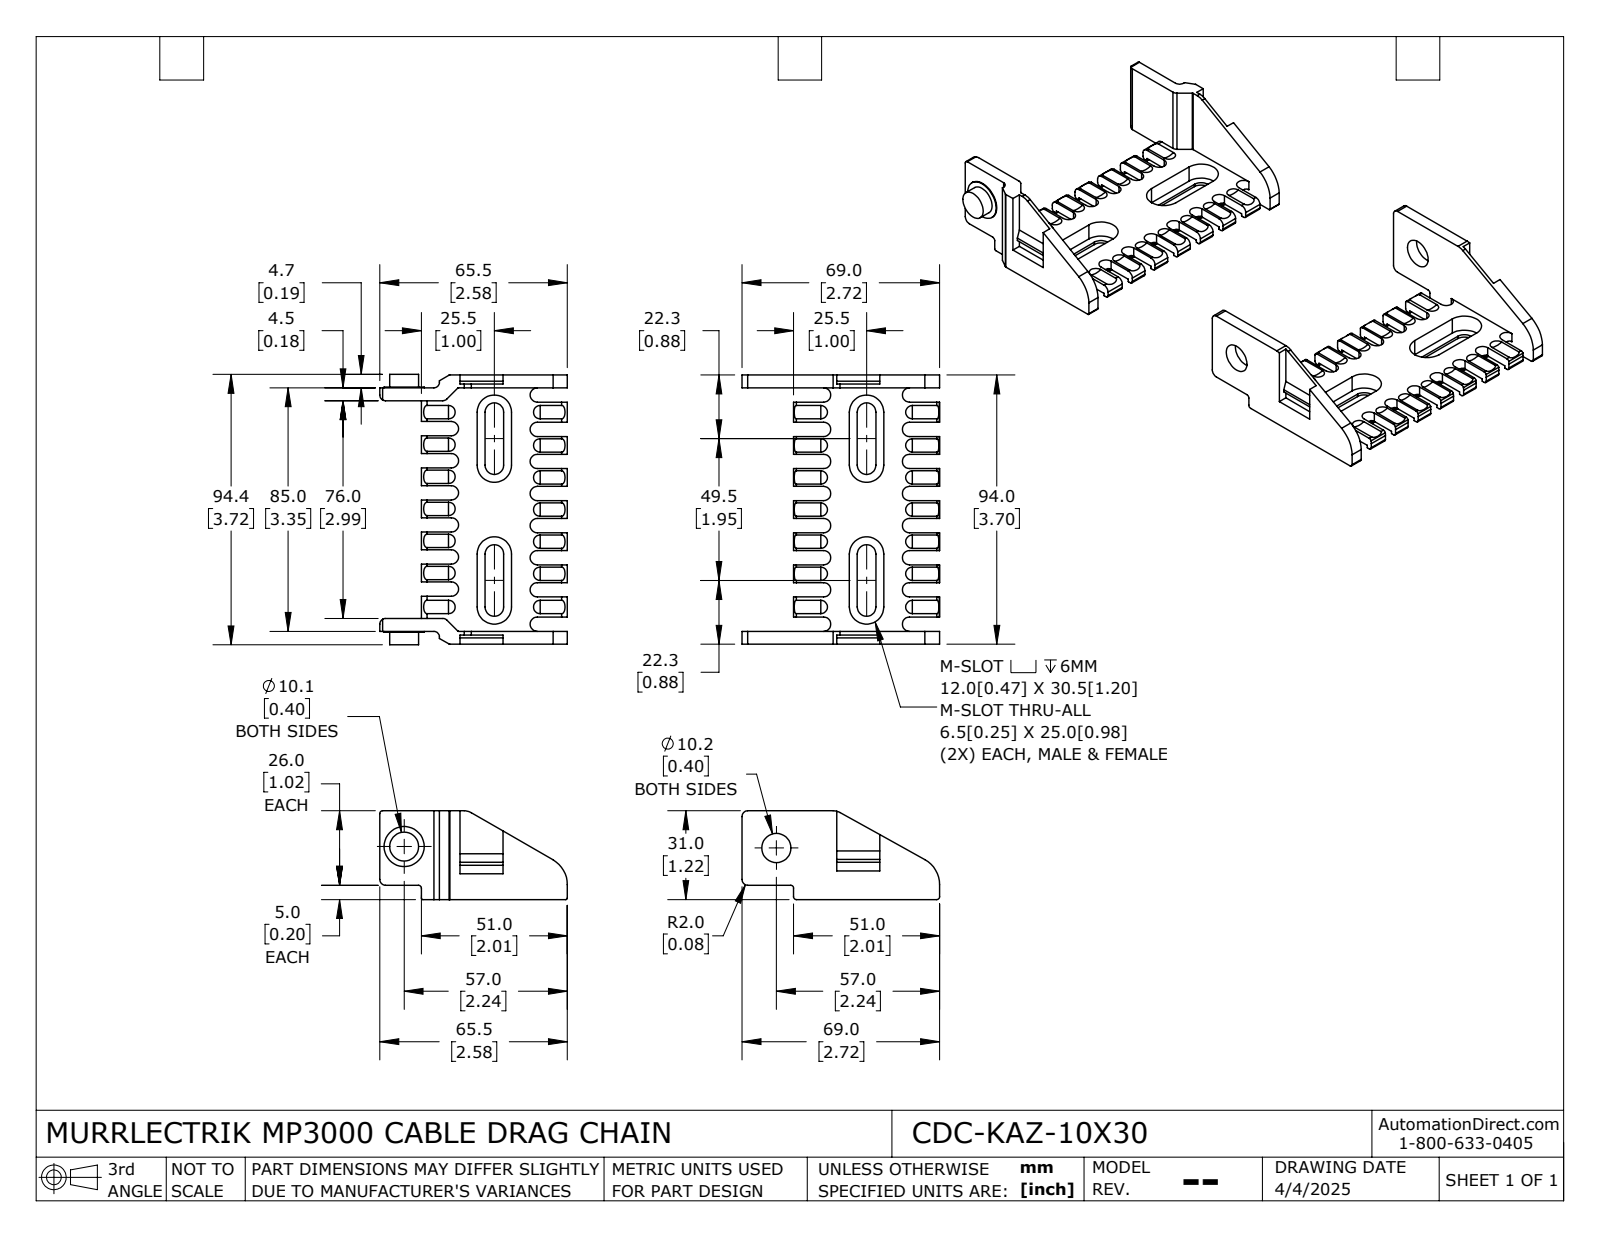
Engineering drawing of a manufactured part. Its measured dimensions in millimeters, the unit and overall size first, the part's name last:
Units: millimetres
Overall size (bounding box): 195.5 × 94.4 × 31
Round holes (diameter × count): ⌀10.2 ×1
Round bosses / shafts (diameter × count): ⌀14 ×1, ⌀10.1 ×1
Partial cylindrical surfaces — rounded edges, fillets, slot ends (radius × count): R2.5 ×30, R1 ×15, R2 ×13, R7 ×12, R3.25 ×8, R6 ×8, R0.5 ×4, R0.1 ×2
Main face-to-face distances: 4.5, 7, 89.5, 85, 3.5, 94, 9, 80.5, 2.5, 5
Volume: 57 043 mm³ · Surface area: 35 248 mm²
Bodies: 2 solids, 547 faces (282 planar, 237 cylindrical, 28 other)
Part name (STEP PRODUCT): CDC-KAZ-10X30
STEP written by: SolidWorks 2024 (AUTOMOTIVE_DESIGN)
